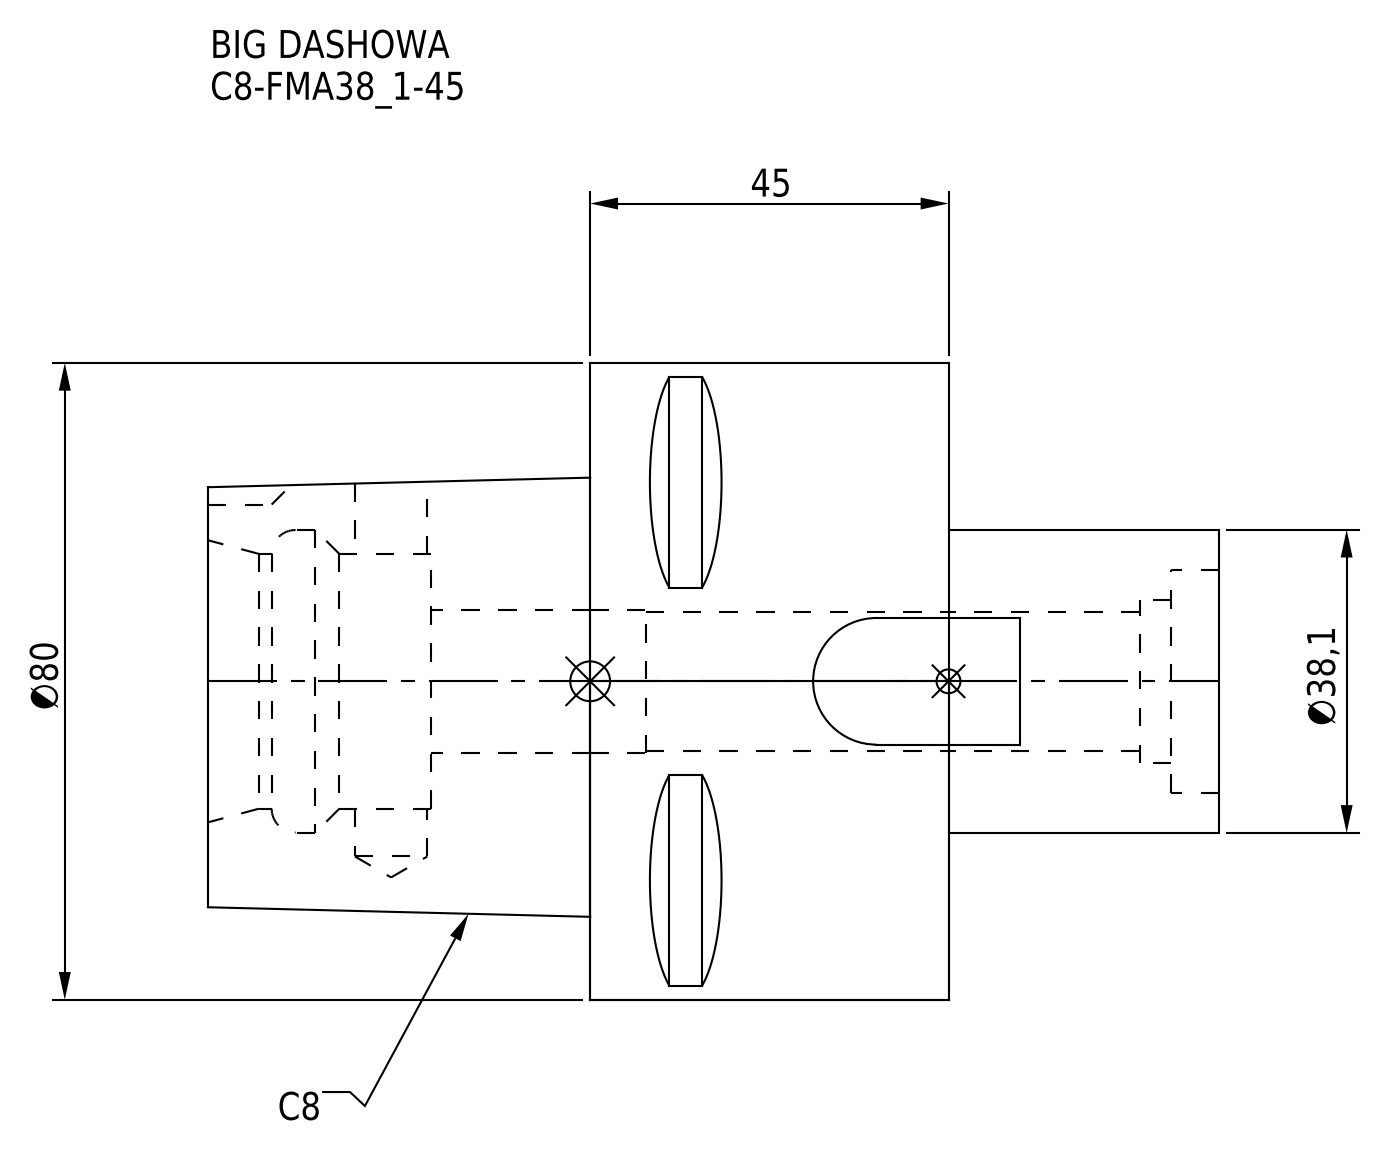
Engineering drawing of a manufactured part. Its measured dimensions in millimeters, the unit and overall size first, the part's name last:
Units: millimetres
Overall size (bounding box): 127 × 80 × 80
Round holes (diameter × count): ⌀9.1 ×1, ⌀17.5 ×1, ⌀18 ×1, ⌀20.5 ×1, ⌀28 ×1, ⌀32 ×1, ⌀38 ×1
Round bosses / shafts (diameter × count): ⌀80 ×1, ⌀38.1 ×1
Partial cylindrical surfaces — rounded edges, fillets, slot ends (radius × count): R6 ×1
Main face-to-face distances: 45, 93, 48, 65, 28, 20, 34, 79, 99, 127
Volume: 321 138 mm³ · Surface area: 43 634 mm²
Bodies: 1 solid, 73 faces (40 planar, 23 cylindrical, 10 other)
Part name (STEP PRODUCT): C8-FMA38_1-45
STEP written by: CREO PARAMETRIC BY PTC INC, 2016380 (AUTOMOTIVE_DESIGN)
